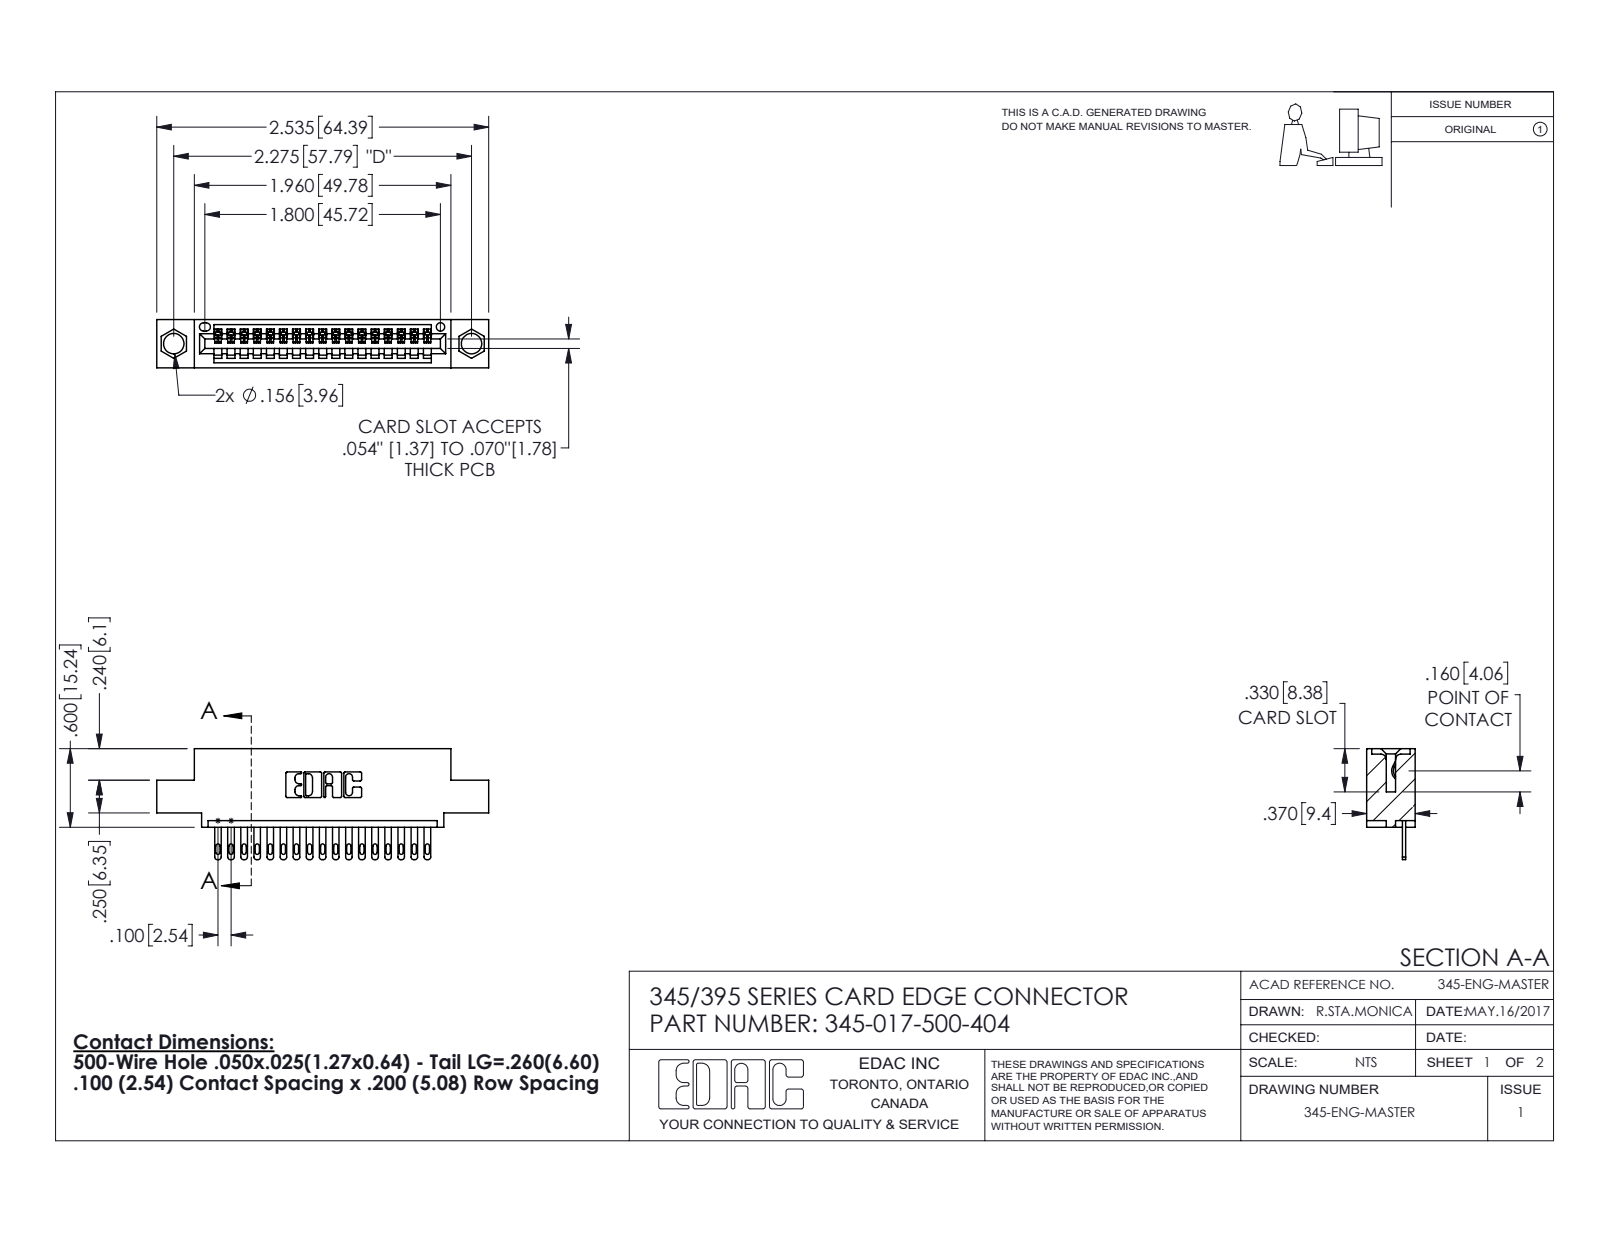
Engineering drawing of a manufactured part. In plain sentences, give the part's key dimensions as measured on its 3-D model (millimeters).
The part is named "345-017-500-404; 345-292-001_345-293-100; 345 Part_0.110 Offset - 0.156 Dia-TH". Its 3-D file was written by "SolidWorks 2016 (CONFIG_CONTROL_DESIGN)". It is 18 solids with 1048 faces: 662 planar, 386 cylindrical and 0 other. Overall it measures 64.4 by 21.5 by 9.4 millimeters. Its volume is 5 770 cubic millimeters and its surface area 7 245 square millimeters. Round holes: 2 of diameter 4, 1 of diameter 1.6. Partial cylindrical surfaces (rounded edges, fillets, slot ends): 34 of radius 0.2, 34 of radius 0.4, 34 of radius 0.5, 22 of radius 0.3, 6 of radius 0.2, 6 of radius 0.8, 3 of radius 0.7, 2 of radius 0.8. The main face-to-face distances are 7.6, 1.8, 5.1, 9.4, 2.5, 6.9, 0.6, 5.7, 2.5, 3.8. The hole center spacings are 6.9, 51.8, 57.8.
